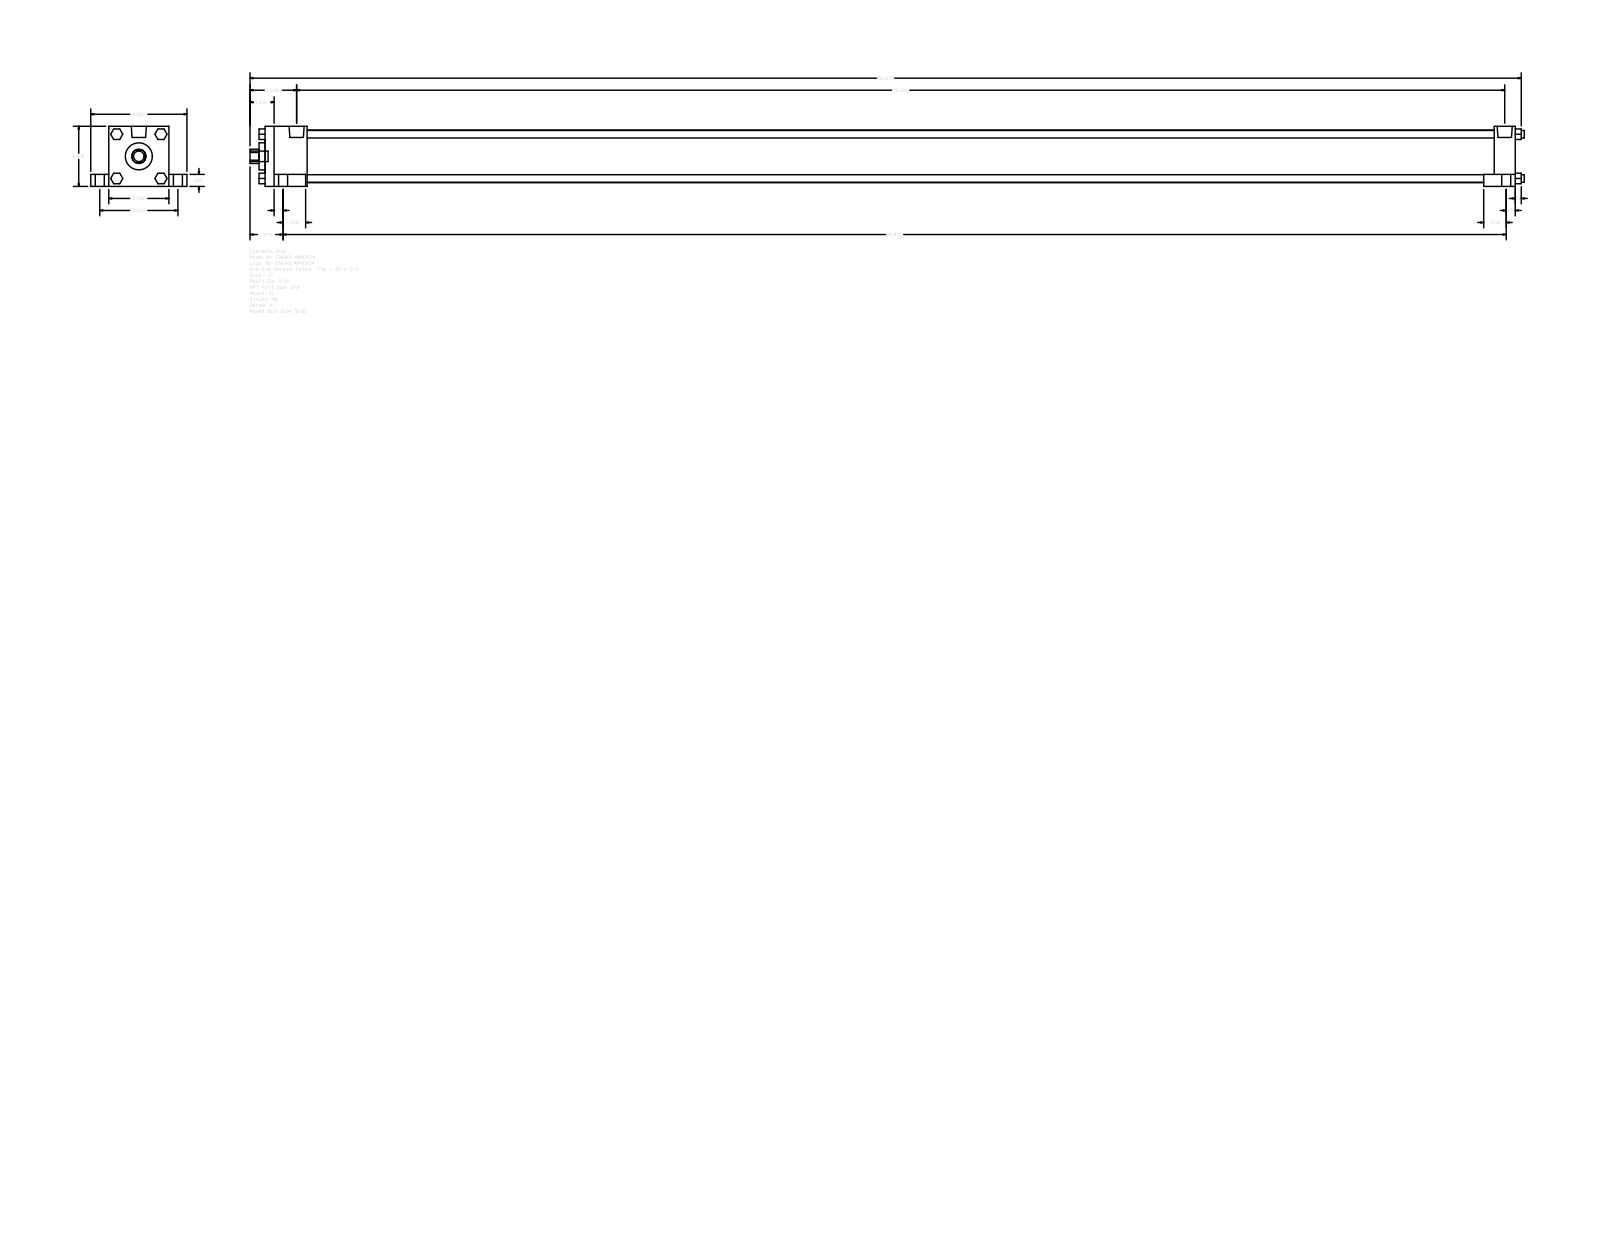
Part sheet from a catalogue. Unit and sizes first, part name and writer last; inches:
Units: inches
Overall size (bounding box): 53 × 4 × 2.5
Round holes (diameter × count): ⌀0.625 ×1, ⌀1.125 ×1, ⌀2.19 ×1
Round bosses / shafts (diameter × count): ⌀0.625 ×4, ⌀0.375 ×4, ⌀0.313 ×4, ⌀0.219 ×4, ⌀0.627 ×2, ⌀0.437 ×1
Partial cylindrical surfaces — rounded edges, fillets, slot ends (radius × count): R0.297 ×1
Main face-to-face distances: 2.5, 52, 2, 0.5, 0.75, 3.25, 1.75, 50.25, 51.125, 49.375
Bodies: 0 solids, 148 faces (112 planar, 36 cylindrical, 0 other)
Part name (STEP PRODUCT): A_SL__0200_0.625
STEP written by: GSSL Pune (CONFIG_CONTROL_DESIGN)
